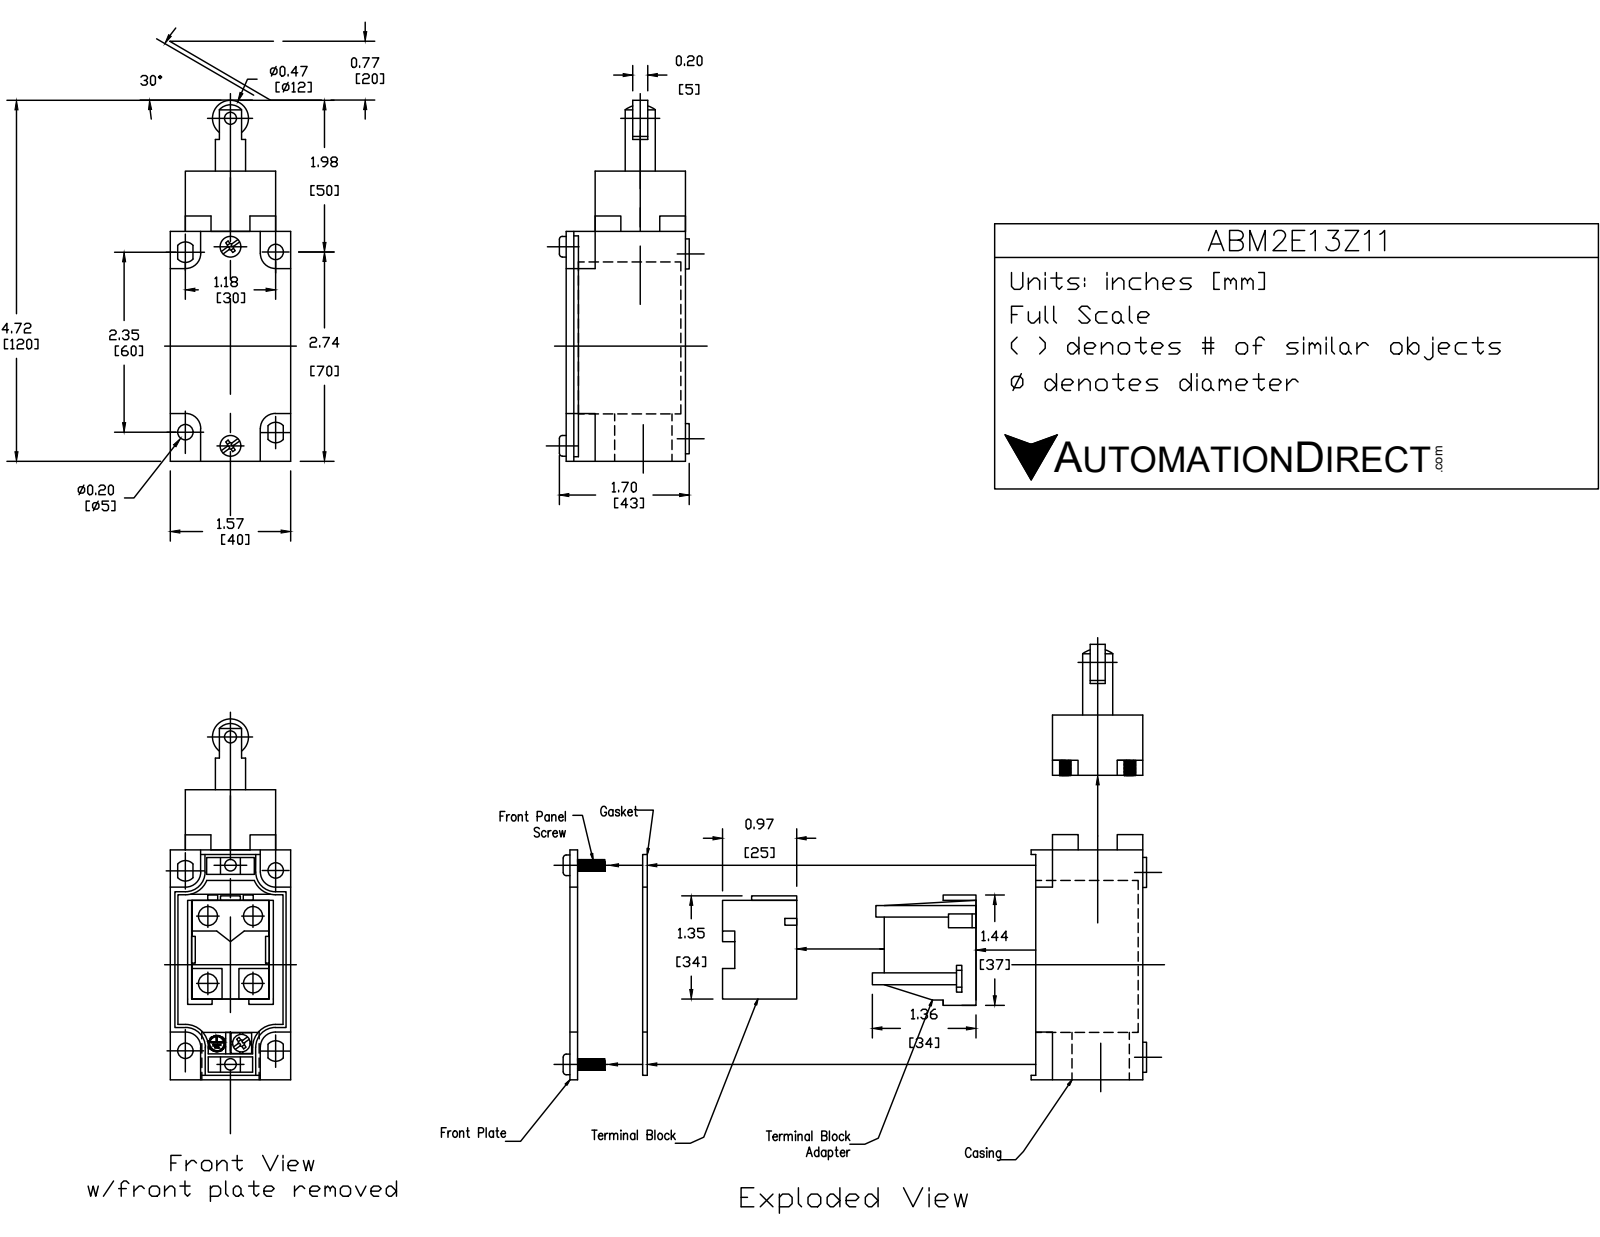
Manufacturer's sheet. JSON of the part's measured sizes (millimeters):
{"part_name": "ABM2E13Z11", "step_written_by": "SolidWorks 2017 (AUTOMOTIVE_DESIGN)", "units": "millimeters", "bodies": {"solids": 4, "faces": 167, "planar": 77, "cylindrical": 68, "other": 22}, "overall_size": [119.9, 43.3, 40], "volume_mm3": 128500, "surface_area_mm2": 25080, "round_holes": [[5.2, 2], [10, 1], [17, 1], [19, 1]], "round_bosses_or_shafts": [[10, 4], [7, 2], [12, 1]], "partial_cylinders_radius": [[1.5, 16], [1, 4], [5, 4], [3.3, 2], [11.5, 1], [12, 1]], "face_to_face_distances": [40, 39.5, 30, 5, 35, 9.5, 76.5, 81.5, 15, 77], "hole_center_spacings": [1, 67.1]}
